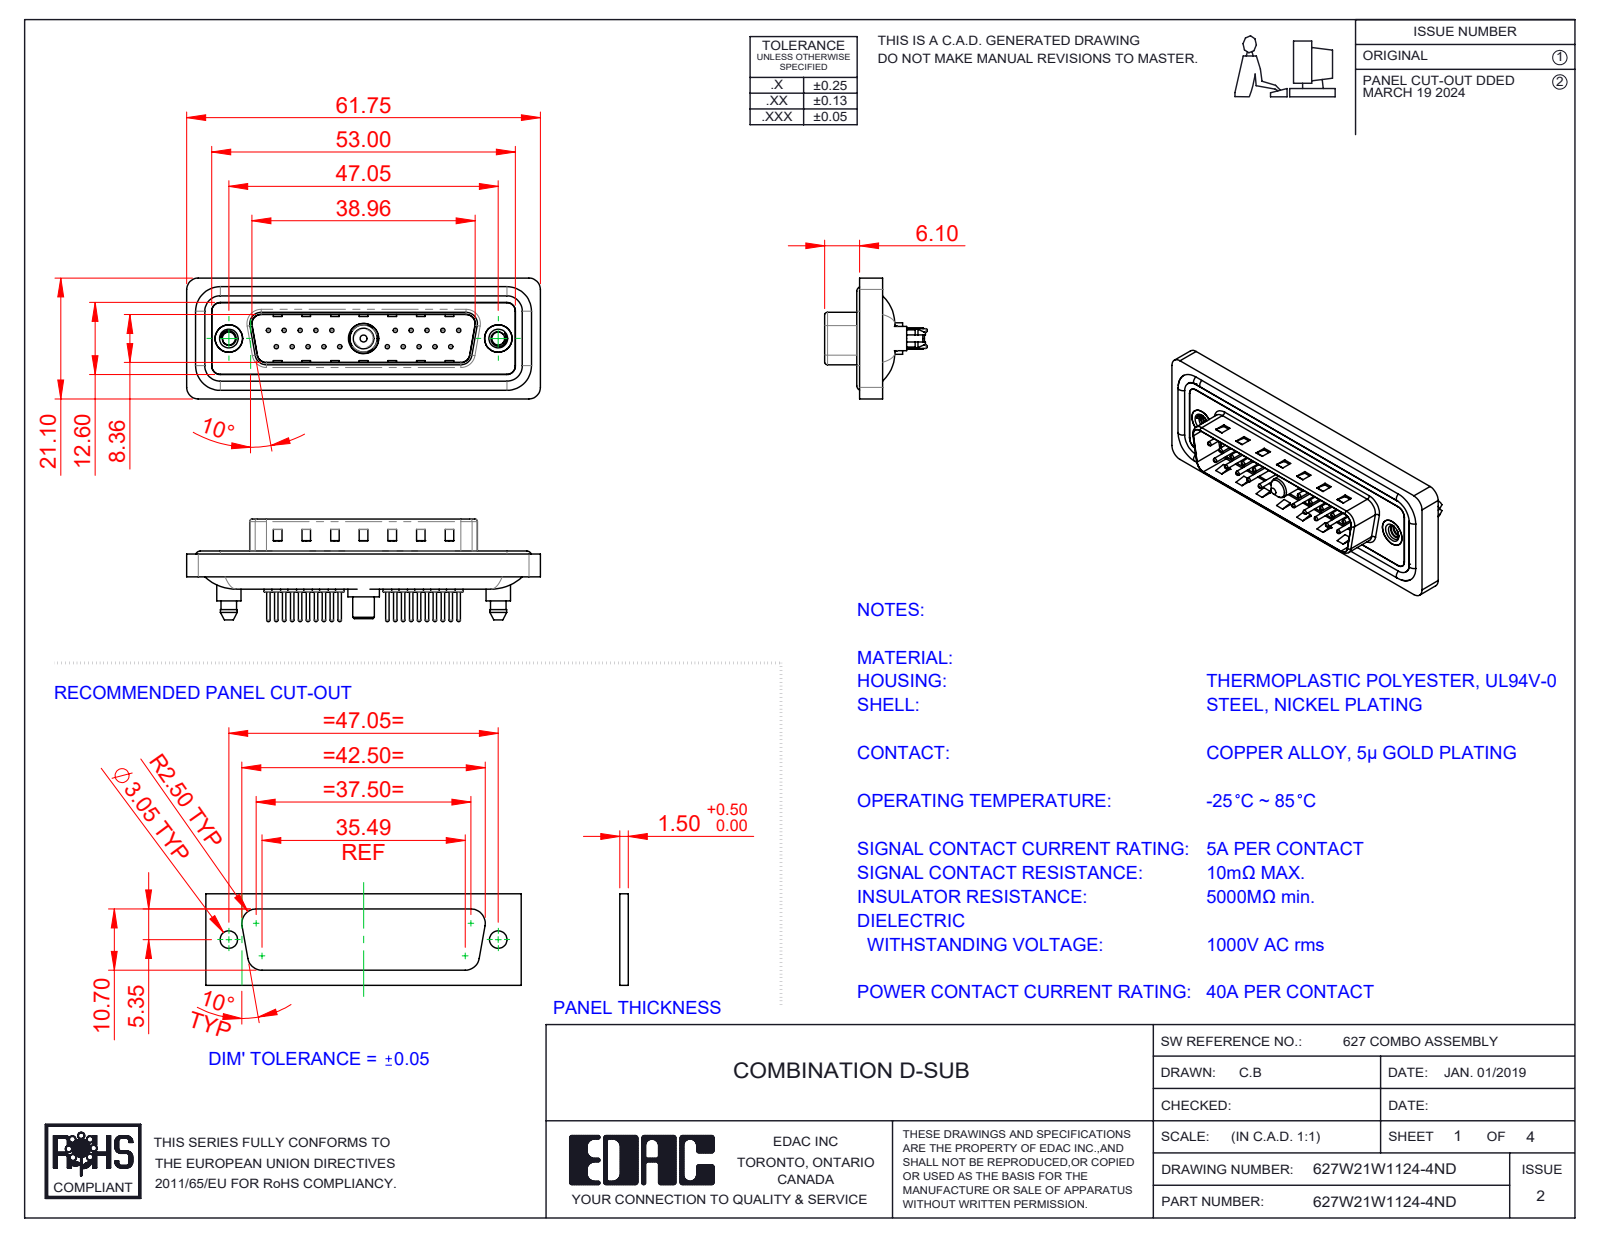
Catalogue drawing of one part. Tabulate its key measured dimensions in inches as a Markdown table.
| quantity | value |
| --- | --- |
| part name | 627Combo Threaded Boardlock_D; 627Combo Shell Rear_25 Contacts; 627Combo Contact Row 1_24; 627Combo Waterproof Housing_25 Contacts (+6 more) |
| STEP written by | SolidWorks 2023 (CONFIG_CONTROL_DESIGN) |
| units | inches |
| bodies | 29 solids, 1320 faces (375 planar, 527 cylindrical, 418 other) |
| overall size | 2.431 × 0.831 × 0.705 |
| volume | 0.449 in³ |
| surface area | 19.07 in² |
| round holes (diameter × count) | 0.03 × 20, 0.063 × 20, 0.079 × 20, 0.089 × 2, 0.157 × 2, 0.189 × 2, 0.197 × 2, 0.191 × 1, 0.209 × 1 |
| round bosses / shafts (diameter × count) | 0.059 × 20, 0.024 × 20, 0.063 × 4, 0.213 × 2, 0.193 × 2, 0.167 × 2, 0.217 × 1, 0.205 × 1 |
| partial cylindrical surfaces (radius × count) | 0.059 × 24, 0.079 × 18, 0.063 × 10, 0.02 × 8, 0.01 × 4, 0.024 × 4, 0.026 × 4, 0.035 × 4 |
| main face-to-face distances | 0.016, 0.059, 0.043, 0.063, 0.122, 0.02, 0.114, 0.161, 0.032, 0.377 |
| hole center spacings | 0.124, 0.109, 0.218, 0.327, 0.198, 0.763, 0.826, 0.872 |
